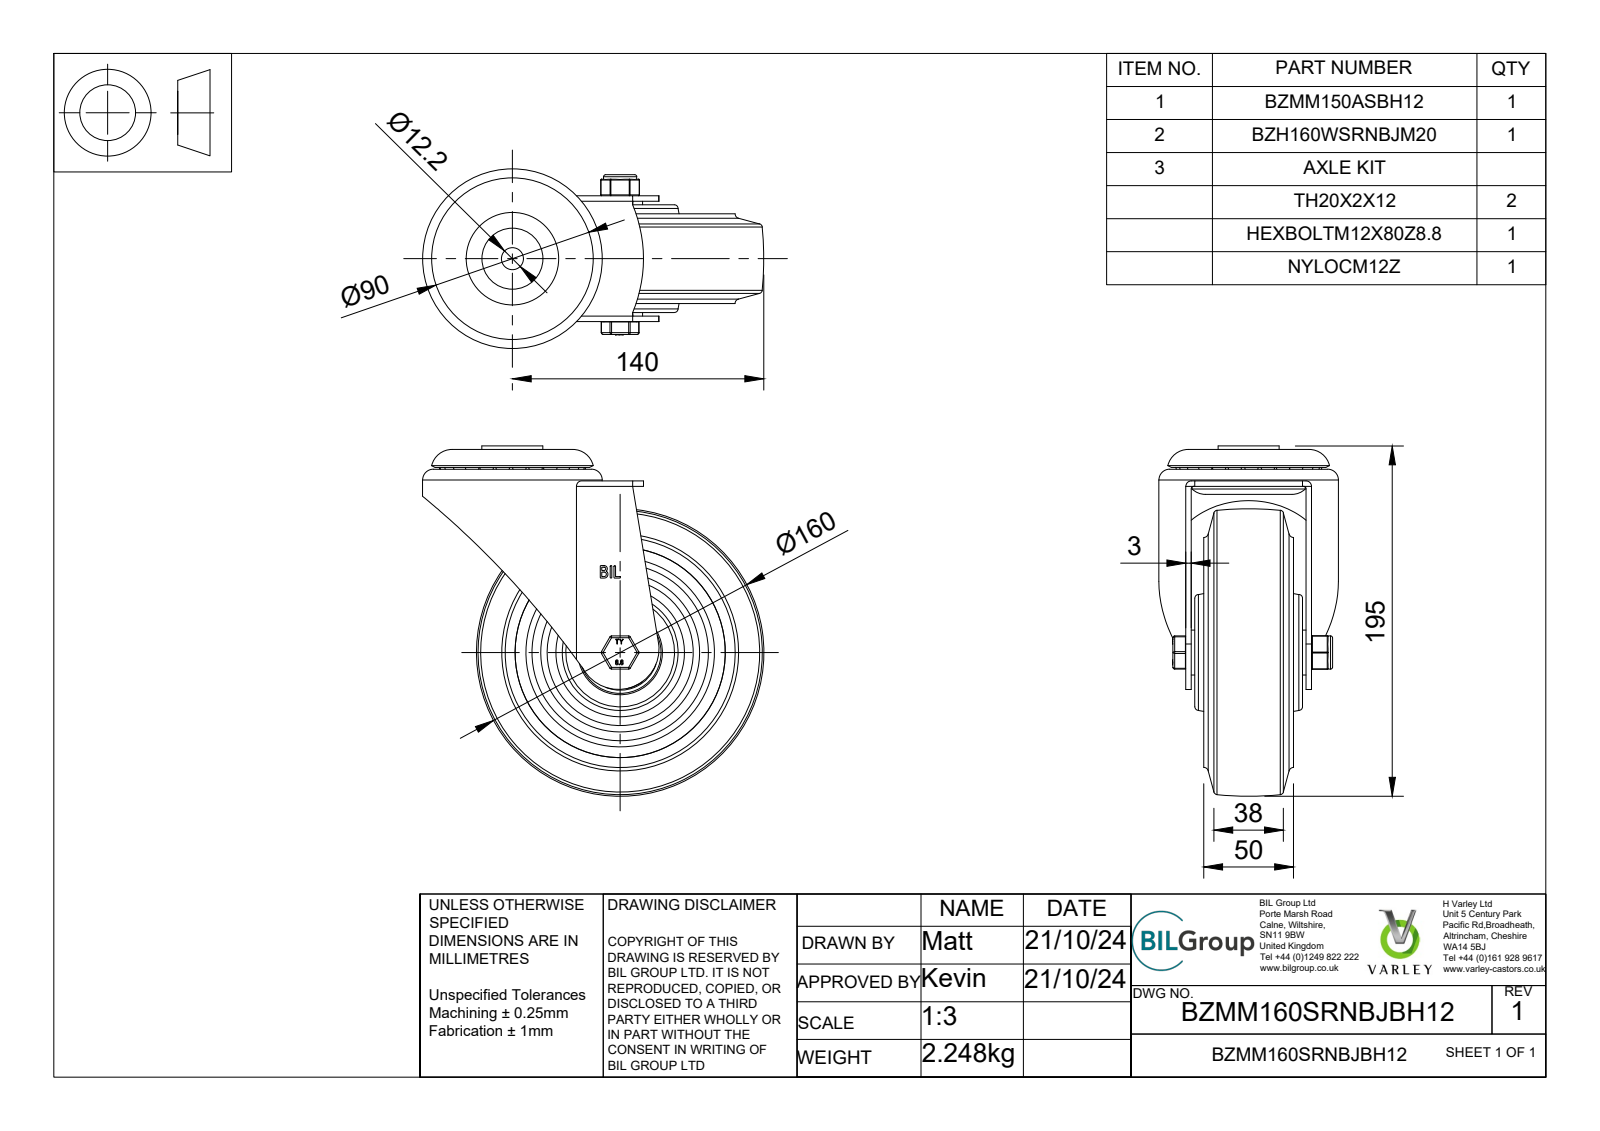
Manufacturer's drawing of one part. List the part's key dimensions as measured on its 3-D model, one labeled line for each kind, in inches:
Part name (STEP PRODUCT): BZMM160SRNBJBH12 v3; BZMM150ASBH12 - 64 v1; ZINC PLATED, PRESSED STEEL FORKS; ZINC PLATED, PRESSED STEEL HEAD (+6 more)
STEP written by: Autodesk Translation Framework v13.20.0.188 (AUTOMOTIVE_DESIGN)
Units: inches
Bodies: 81 solids, 1085 faces (402 planar, 187 cylindrical, 496 other)
Overall size (bounding box): 7.677 × 7.48 × 3.937
Volume: 55.78 in³ · Surface area: 401.9 in²
Round holes (diameter × count): ⌀0.48 ×2, ⌀0.472 ×1, ⌀0.492 ×1, ⌀0.551 ×1, ⌀0.787 ×1, ⌀1.122 ×1, ⌀1.213 ×1, ⌀1.535 ×1, ⌀1.575 ×1, ⌀1.587 ×1, ⌀1.594 ×1, ⌀1.654 ×1
Round bosses / shafts (diameter × count): ⌀0.945 ×2, ⌀3.937 ×1, ⌀2.48 ×1, ⌀1.606 ×1, ⌀1.339 ×1, ⌀1.232 ×1, ⌀1.063 ×1, ⌀0.984 ×1
Partial cylindrical surfaces — rounded edges, fillets, slot ends (radius × count): R0.02 ×18, R0.039 ×12, R0.059 ×4, R0.118 ×2, R0.65 ×1, R0.768 ×1, R0.888 ×1, R3.071 ×1
Main face-to-face distances: 0.118, 2.362, 0.394, 0.276, 0.197, 2.638, 2.244, 2.52, 2.756, 0.02
